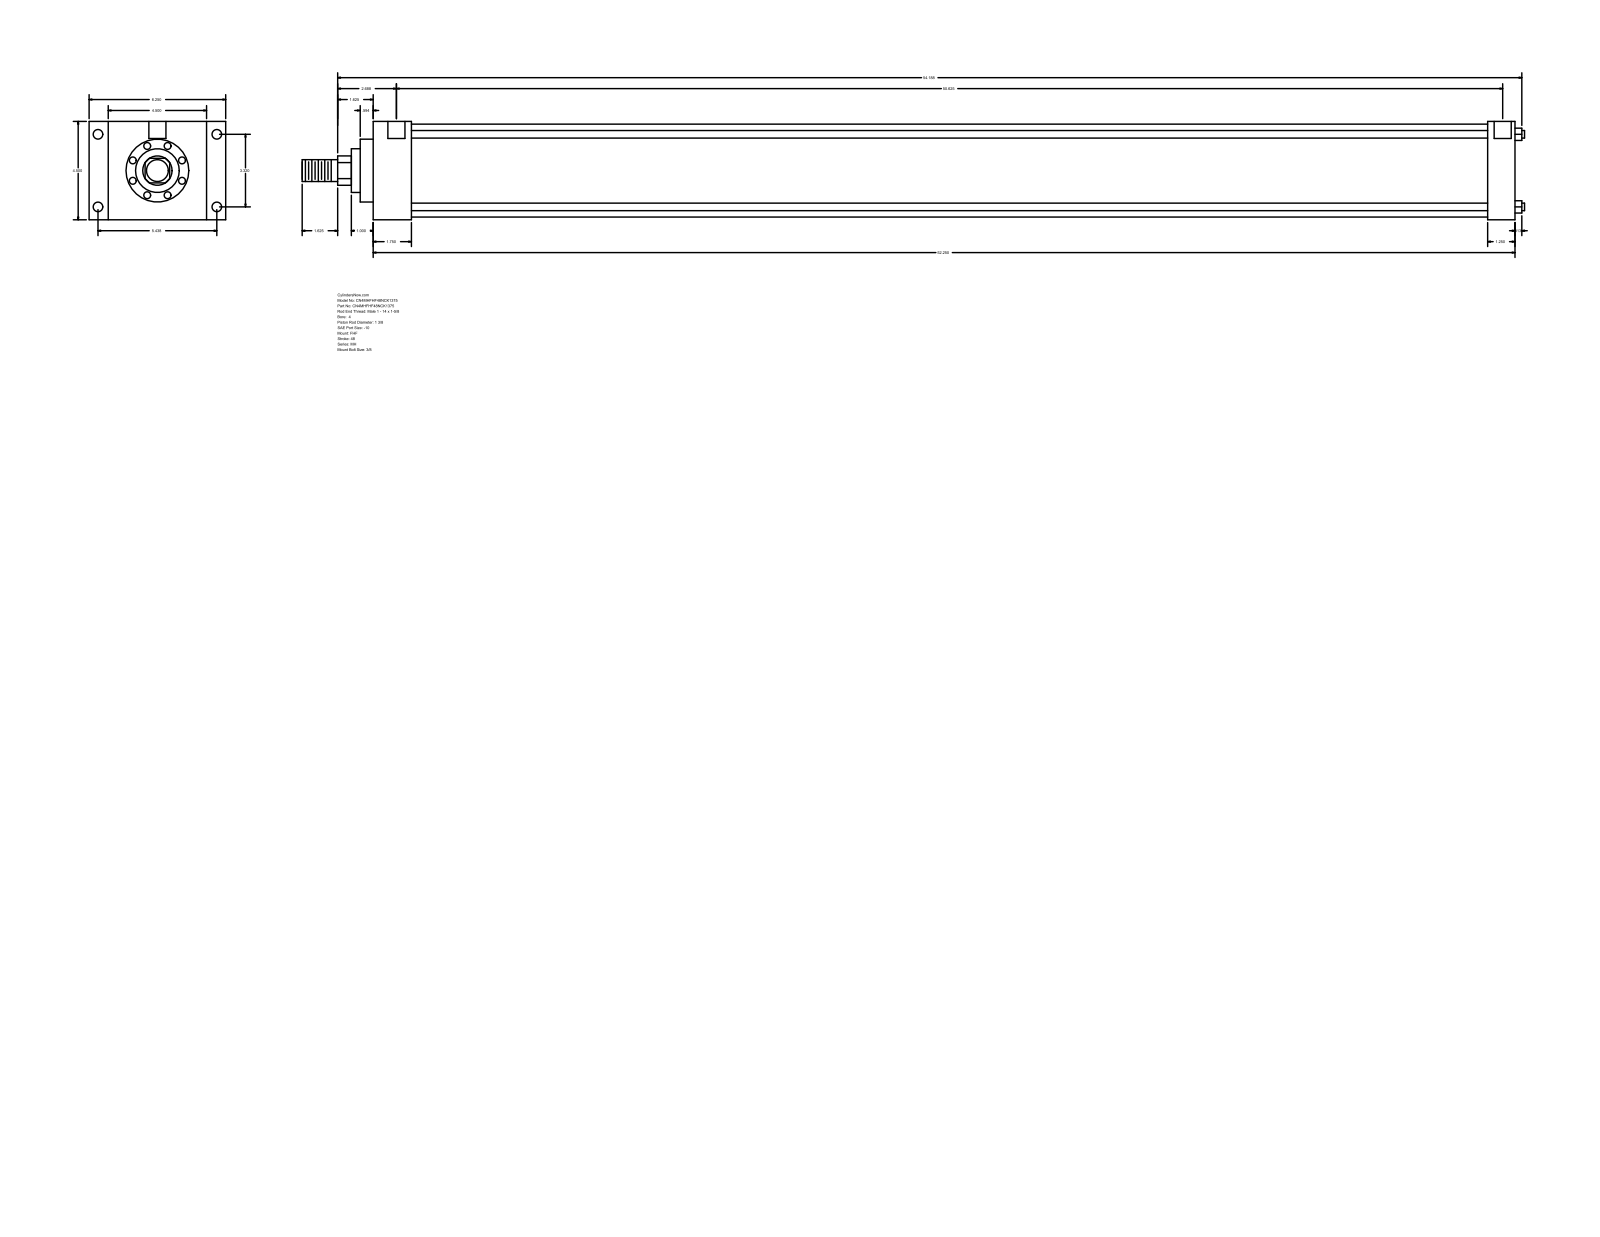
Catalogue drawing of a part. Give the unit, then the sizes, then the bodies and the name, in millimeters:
Units: millimetres
Overall size (bounding box): 1420.81 × 158.75 × 114.3
Round holes (diameter × count): ⌀8.73 ×4, ⌀11.13 ×4, ⌀19.84 ×2
Round bosses / shafts (diameter × count): ⌀8.76 ×4, ⌀107.95 ×1, ⌀73.03 ×1, ⌀50.8 ×1, ⌀34.92 ×1, ⌀25.4 ×1
Partial cylindrical surfaces — rounded edges, fillets, slot ends (radius × count): R17.06 ×1
Main face-to-face distances: 114.3, 1327.15, 44.45, 1282.7, 22.23, 136.53, 158.76, 1295.4, 1250.95, 31.75
Hole centre spacings: 84.32, 138.12, 161.82, 1289.05, 1.58, 1.59, 1285.88, 1287.46
Bodies: 0 solids, 90 faces (61 planar, 29 cylindrical, 0 other)
Part name (STEP PRODUCT): MH_FHF__0400_1.375
STEP written by: GSSL Pune (CONFIG_CONTROL_DESIGN)
